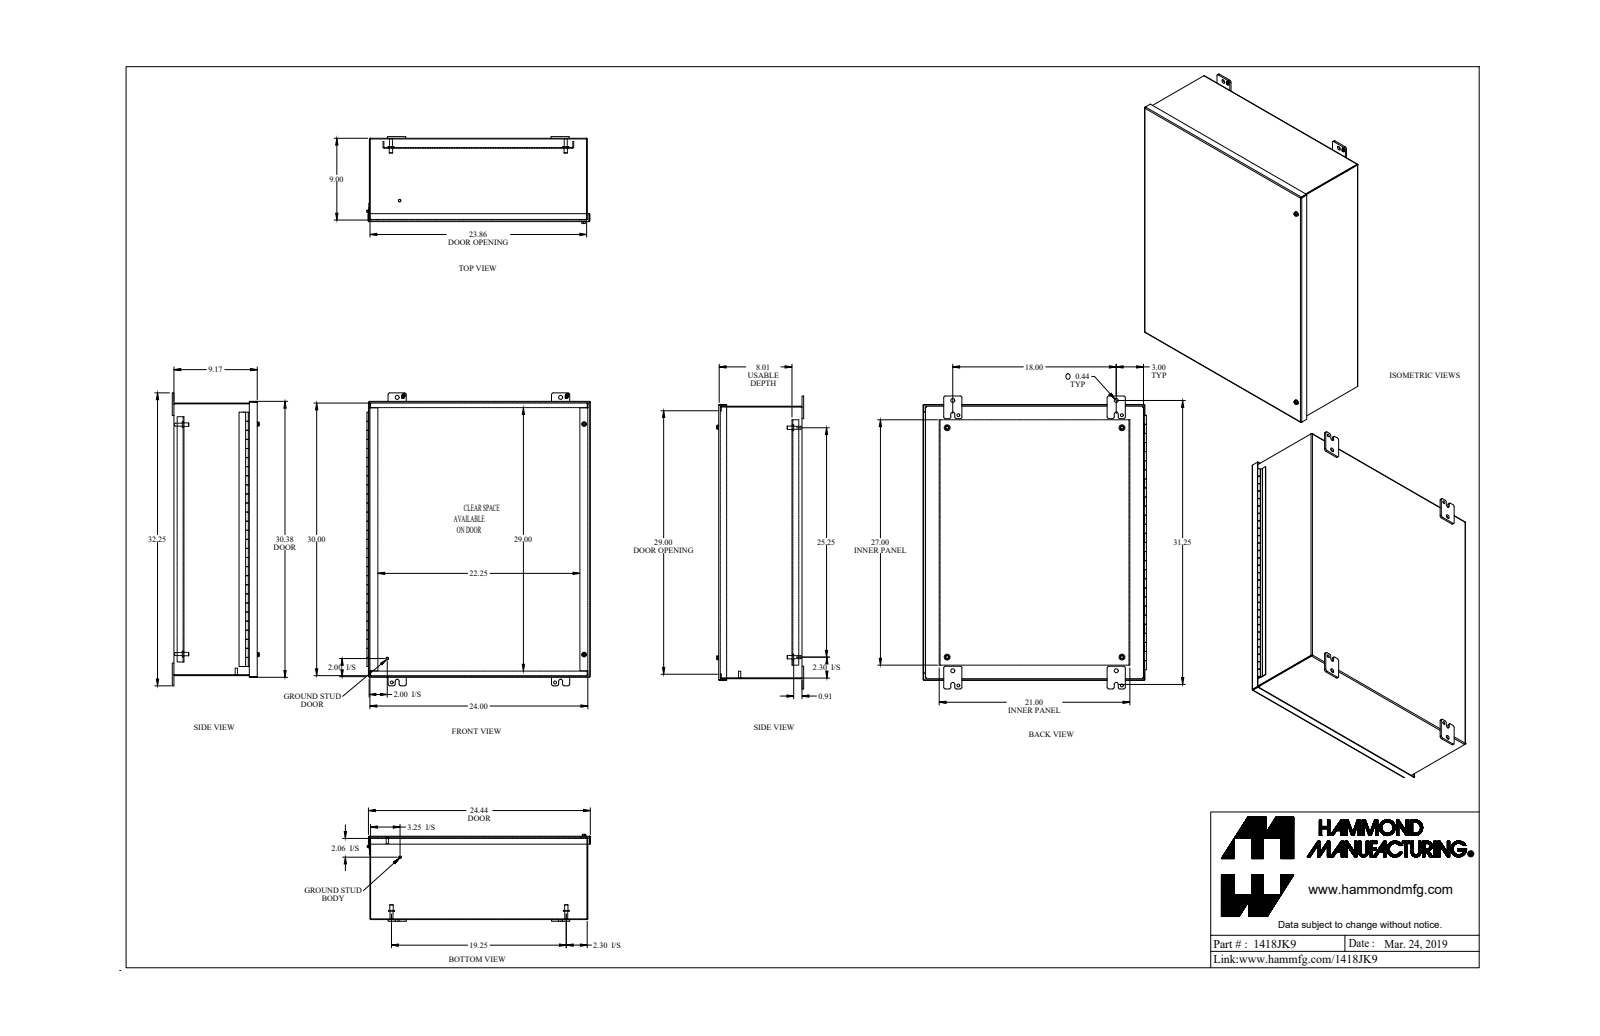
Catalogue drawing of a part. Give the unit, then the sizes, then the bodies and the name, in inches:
Units: inches
Overall size (bounding box): 32.25 × 24.604 × 9.571
Round holes (diameter × count): ⌀0.313 ×6, ⌀0.437 ×4, ⌀0.5 ×4, ⌀0.26 ×2, ⌀0.266 ×2, ⌀0.28 ×2, ⌀0.29 ×2, ⌀0.307 ×2, ⌀0.397 ×2, ⌀0.187 ×1, ⌀0.445 ×1, ⌀0.445 ×1
Round bosses / shafts (diameter × count): ⌀0.65 ×4, ⌀0.375 ×4, ⌀0.33 ×4, ⌀1 ×2, ⌀0.51 ×2, ⌀0.5 ×2, ⌀0.39 ×2, ⌀0.281 ×2
Partial cylindrical surfaces — rounded edges, fillets, slot ends (radius × count): R0.188 ×24, R0.25 ×20, R0.036 ×12, R0.108 ×12, R0.218 ×8, R0.133 ×6, R0.06 ×5, R0.125 ×4
Main face-to-face distances: 0.072, 9.1, 9.172, 9.028, 0.095, 7.996, 8.091, 1.104, 1.032, 8.068
Hole centre spacings: 1.736, 18, 29.75, 34.772, 1.907, 1.966, 3.065, 19.25
Volume: 279.4 in³ · Surface area: 6 938 in²
Bodies: 32 solids, 978 faces (599 planar, 337 cylindrical, 42 other)
Part name (STEP PRODUCT): 1418JK9_Default
STEP written by: SolidWorks 2018 (CONFIG_CONTROL_DESIGN)
